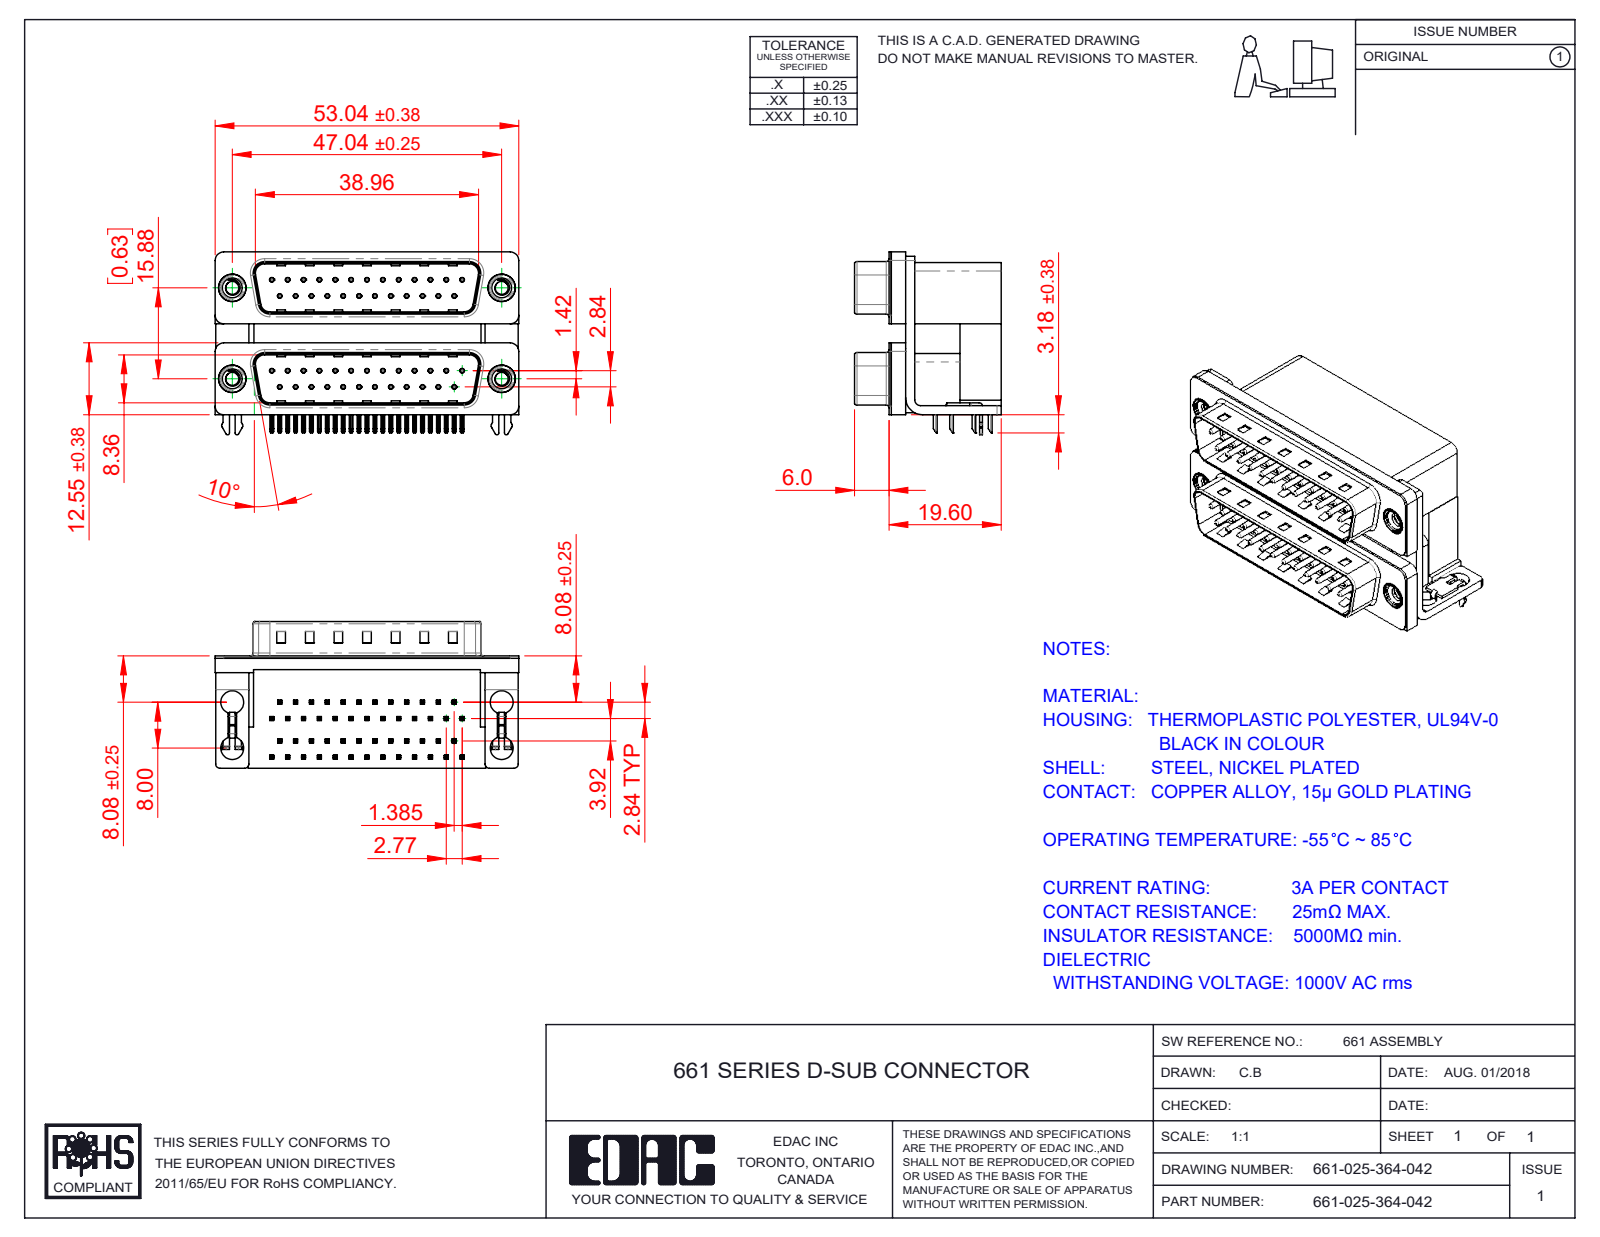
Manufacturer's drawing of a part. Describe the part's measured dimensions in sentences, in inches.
The part is named "661 Contact Bottom Upper_L; 661 Mounting Bracket_ThruL; 661 Contact Top Lower; 661 Housing Upper_25 Contacts L (+8 more)". Its 3-D file was written by "SolidWorks 2020 (CONFIG_CONTROL_DESIGN)". It is 65 solids with 4806 faces: 3034 planar, 1346 cylindrical and 426 other. Overall it measures 2.088 by 1.249 by 1.008 inches. Its volume is 1.242 cubic inches and its surface area 33.52 square inches. Round holes: 50 of diameter 0.014, 50 of diameter 0.031, 4 of diameter 0.079, 4 of diameter 0.089, 4 of diameter 0.098, 4 of diameter 0.126, 4 of diameter 0.138, 4 of diameter 0.157, 4 of diameter 0.189, 4 of diameter 0.197. Round bosses or shafts: 50 of diameter 0.03, 4 of diameter 0.193, 4 of diameter 0.187, 4 of diameter 0.157, 4 of diameter 0.154, 4 of diameter 0.134, 4 of diameter 0.13, 4 of diameter 0.114. Partial cylindrical surfaces (rounded edges, fillets, slot ends): 200 of radius 0.01, 100 of radius 0.005, 16 of radius 0.02, 13 of radius 0.059, 8 of radius 0.03, 8 of radius 0.035, 8 of radius 0.063, 8 of radius 0.079. The main face-to-face distances are 0.016, 0.756, 0.283, 0.472, 0.421, 0.625, 0.657, 0.374, 0.098, 0.611. The hole center spacings are 0.124, 0.109, 0.218, 0.327, 0.436, 0.545, 0.654, 0.198.
